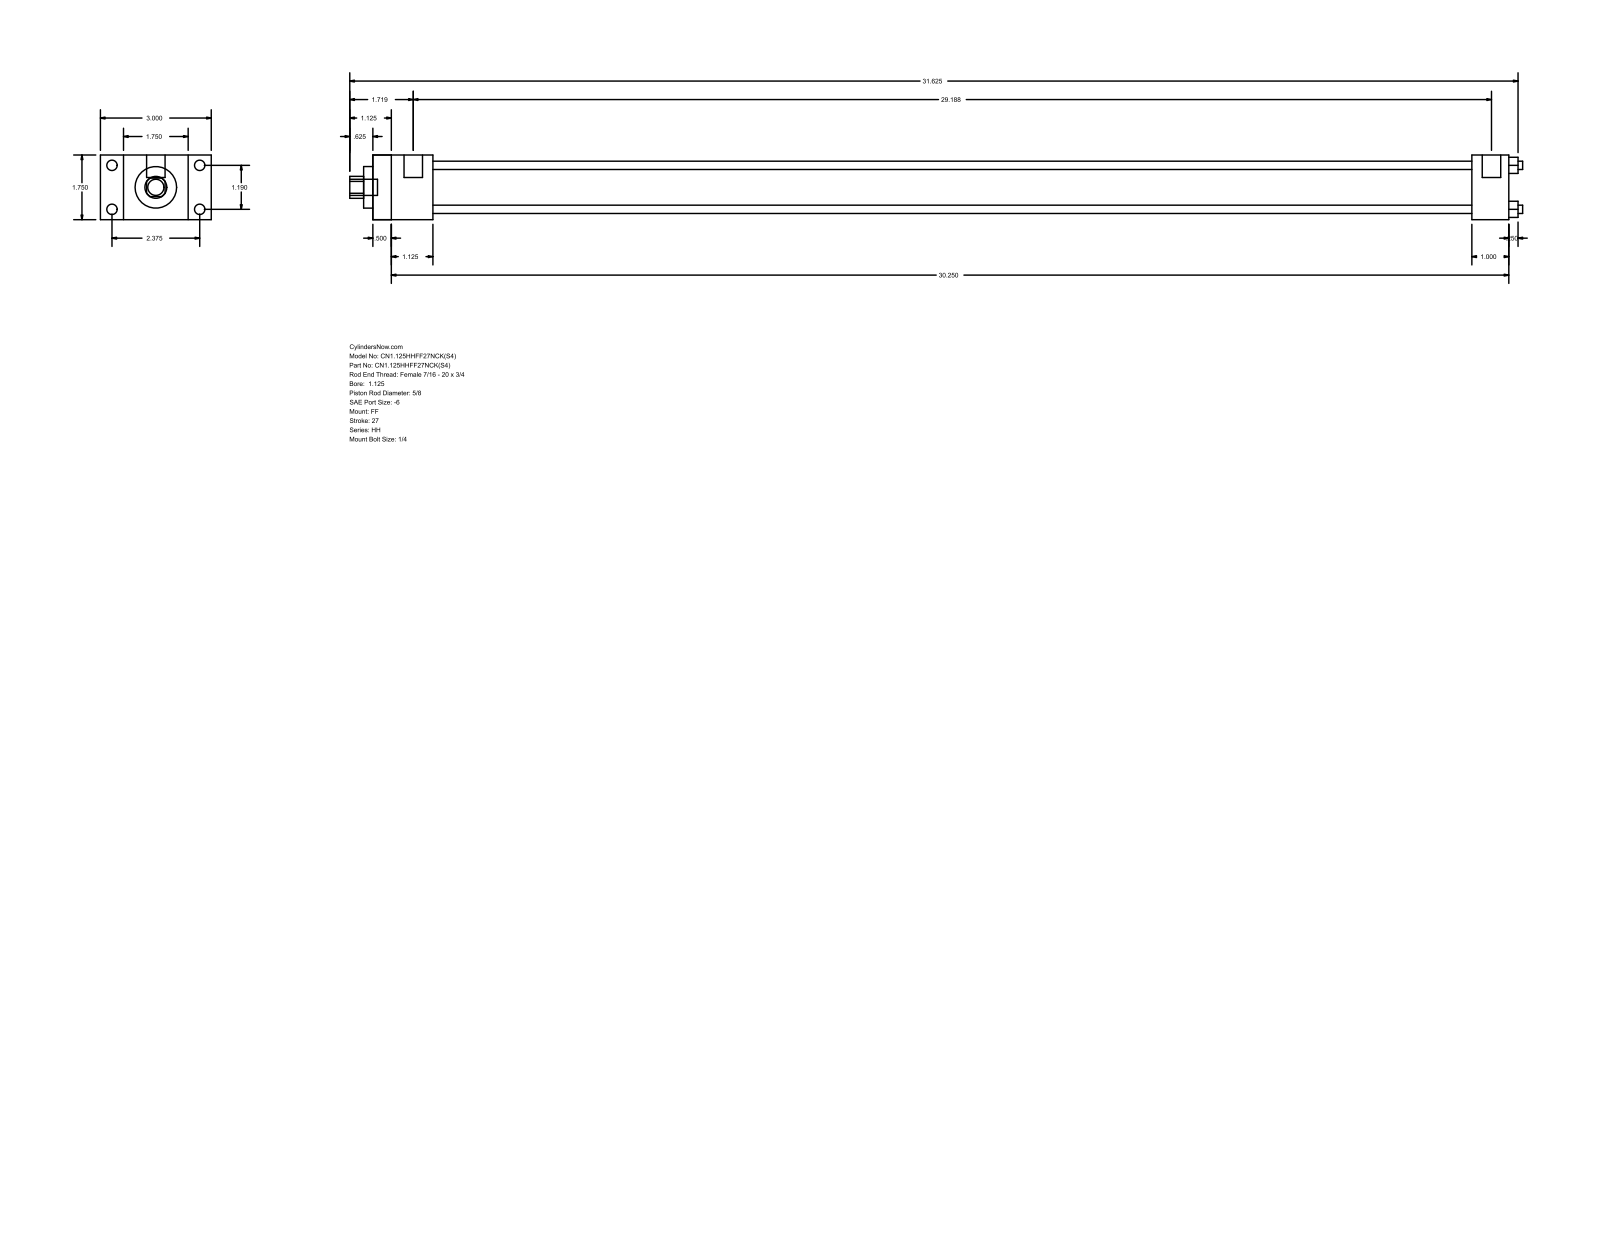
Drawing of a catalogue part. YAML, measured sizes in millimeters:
part_name: "HH_FF__0112_0.625"
step_written_by: "GSSL Pune (CONFIG_CONTROL_DESIGN)"
units: millimeters
bodies: {solids: 0, faces: 92, planar: 64, cylindrical: 28, other: 0}
overall_size: [806.45, 76.2, 44.45]
round_holes:
  - {diameter: 5.71, count: 4}
  - {diameter: 15.88, count: 1}
  - {diameter: 28.57, count: 1}
  - {diameter: 34.92, count: 1}
round_bosses_or_shafts:
  - {diameter: 7.14, count: 4}
  - {diameter: 5.56, count: 4}
  - {diameter: 12.7, count: 2}
  - {diameter: 11.11, count: 1}
partial_cylinders:
  - {radius: 7.54, count: 1}
face_to_face_distances: [44.46, 781.04, 15.87, 12.69, 768.35, 60.33, 28.58, 41.27, 755.64, 742.95]
hole_center_spacings: [21.37, 30.22, 42.74]
